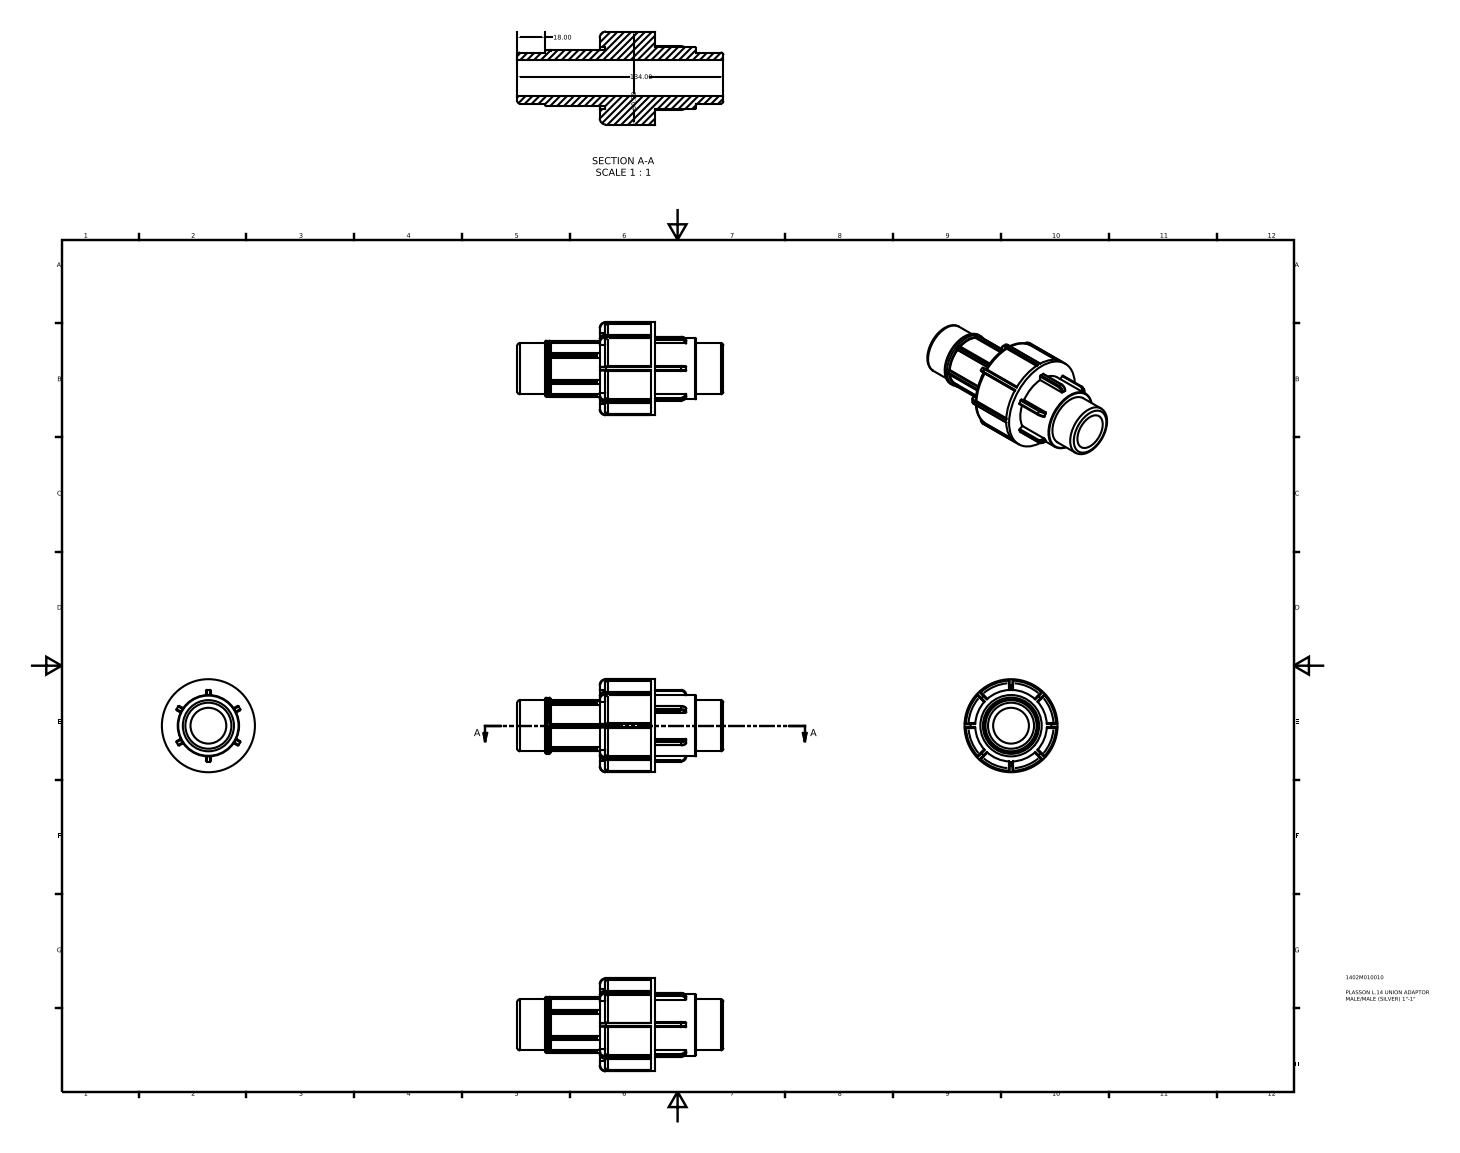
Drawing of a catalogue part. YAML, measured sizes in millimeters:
part_name: "1402M010010"
step_written_by: "Autodesk Inventor 2015 (AUTOMOTIVE_DESIGN)"
units: millimeters
bodies: {solids: 1, faces: 297, planar: 92, cylindrical: 140, other: 65}
overall_size: [134, 60.5, 60.5]
volume: 134733
surface_area: 34678
round_holes:
  - {diameter: 23.27, count: 1}
  - {diameter: 39.9, count: 1}
round_bosses_or_shafts:
  - {diameter: 60.5, count: 1}
  - {diameter: 58.69, count: 1}
  - {diameter: 46.55, count: 1}
  - {diameter: 36.57, count: 1}
  - {diameter: 33.25, count: 1}
partial_cylinders:
  - {radius: 0.3, count: 54}
  - {radius: 0.67, count: 18}
  - {radius: 1, count: 12}
  - {radius: 3.33, count: 6}
face_to_face_distances: [32.58, 3.6, 36.18, 116, 18, 62.4, 58.8, 26.22, 3.32, 53.6]
